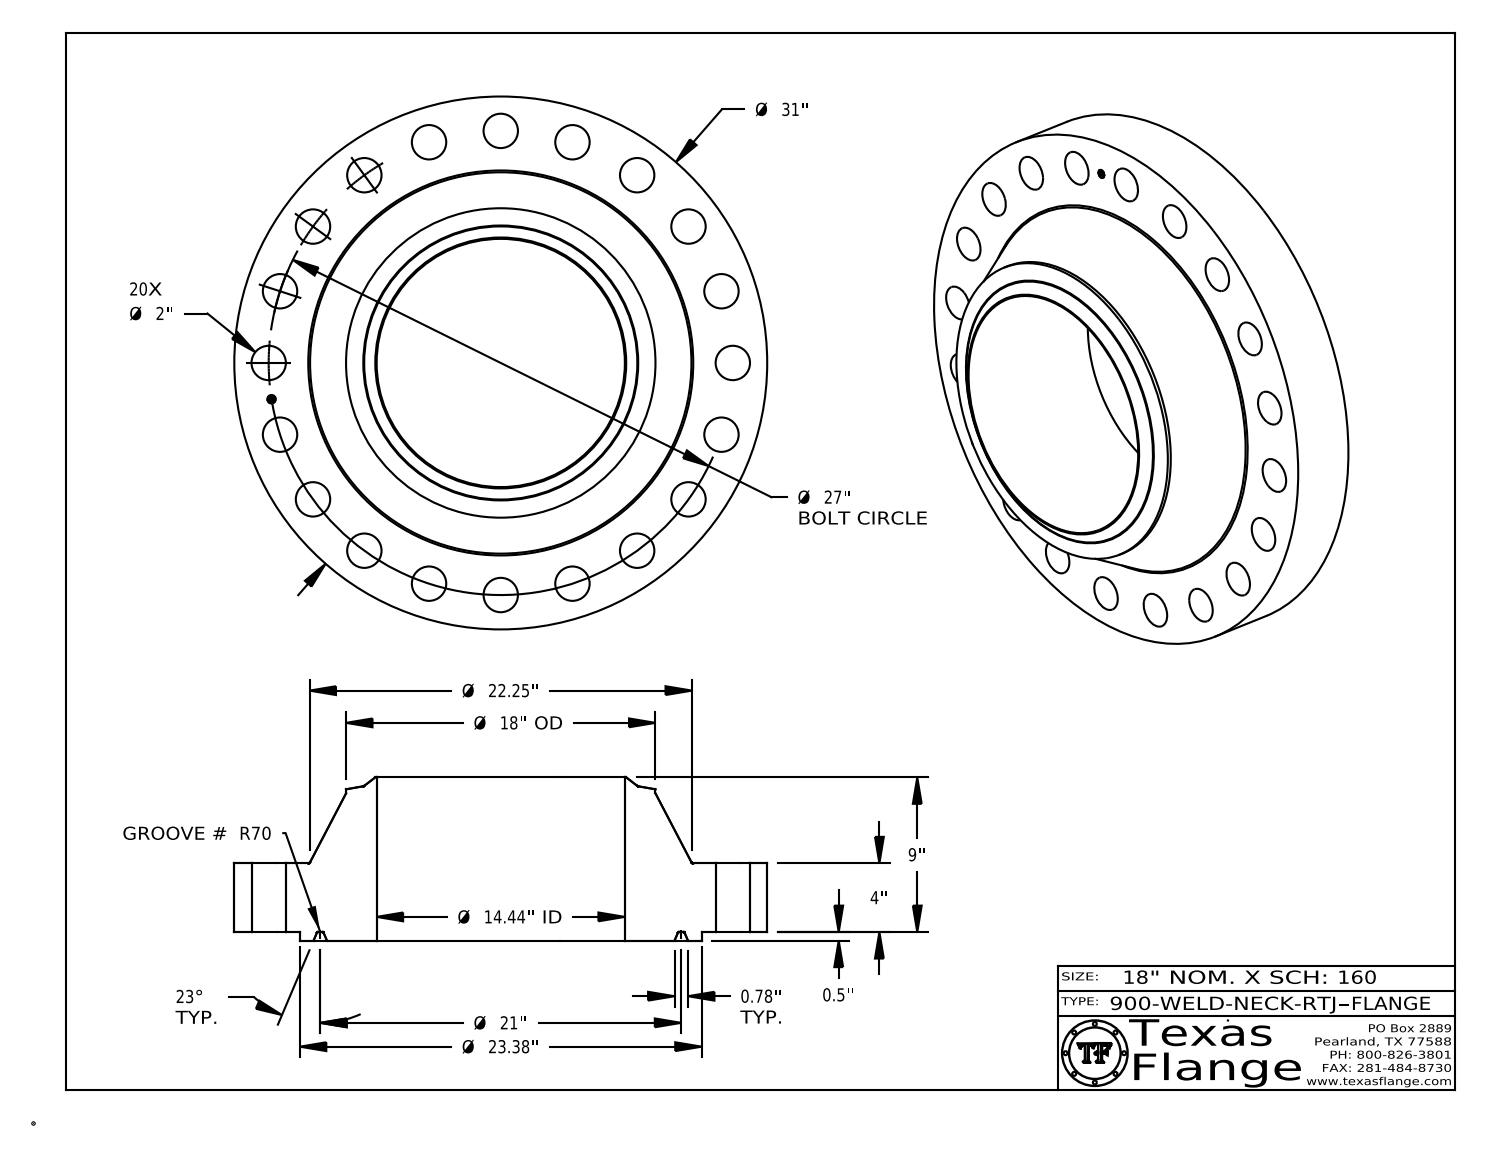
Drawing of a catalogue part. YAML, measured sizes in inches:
part_name: "900-WELD-NECK-RTJ"
step_written_by: "CATIA V5 STEP AP214 (AUTOMOTIVE_DESIGN)"
units: inches
bodies: {solids: 1, faces: 457, planar: 371, cylindrical: 68, other: 18}
overall_size: [31, 31, 9.5]
volume: 2903
surface_area: 2636
round_holes:
  - {diameter: 2, count: 20}
  - {diameter: 0.495, count: 1}
  - {diameter: 14.438, count: 1}
round_bosses_or_shafts:
  - {diameter: 0.03, count: 8}
  - {diameter: 31, count: 1}
  - {diameter: 23.375, count: 1}
  - {diameter: 18, count: 1}
  - {diameter: 0.39, count: 1}
face_to_face_distances: [4, 0.5, 4.5, 9.5, 9, 5, 4.485, 3.985, 0.015, 5.015]
hole_center_spacings: [13.5, 21.843, 24.057, 25.678, 26.668, 4.224, 8.343, 12.258]
